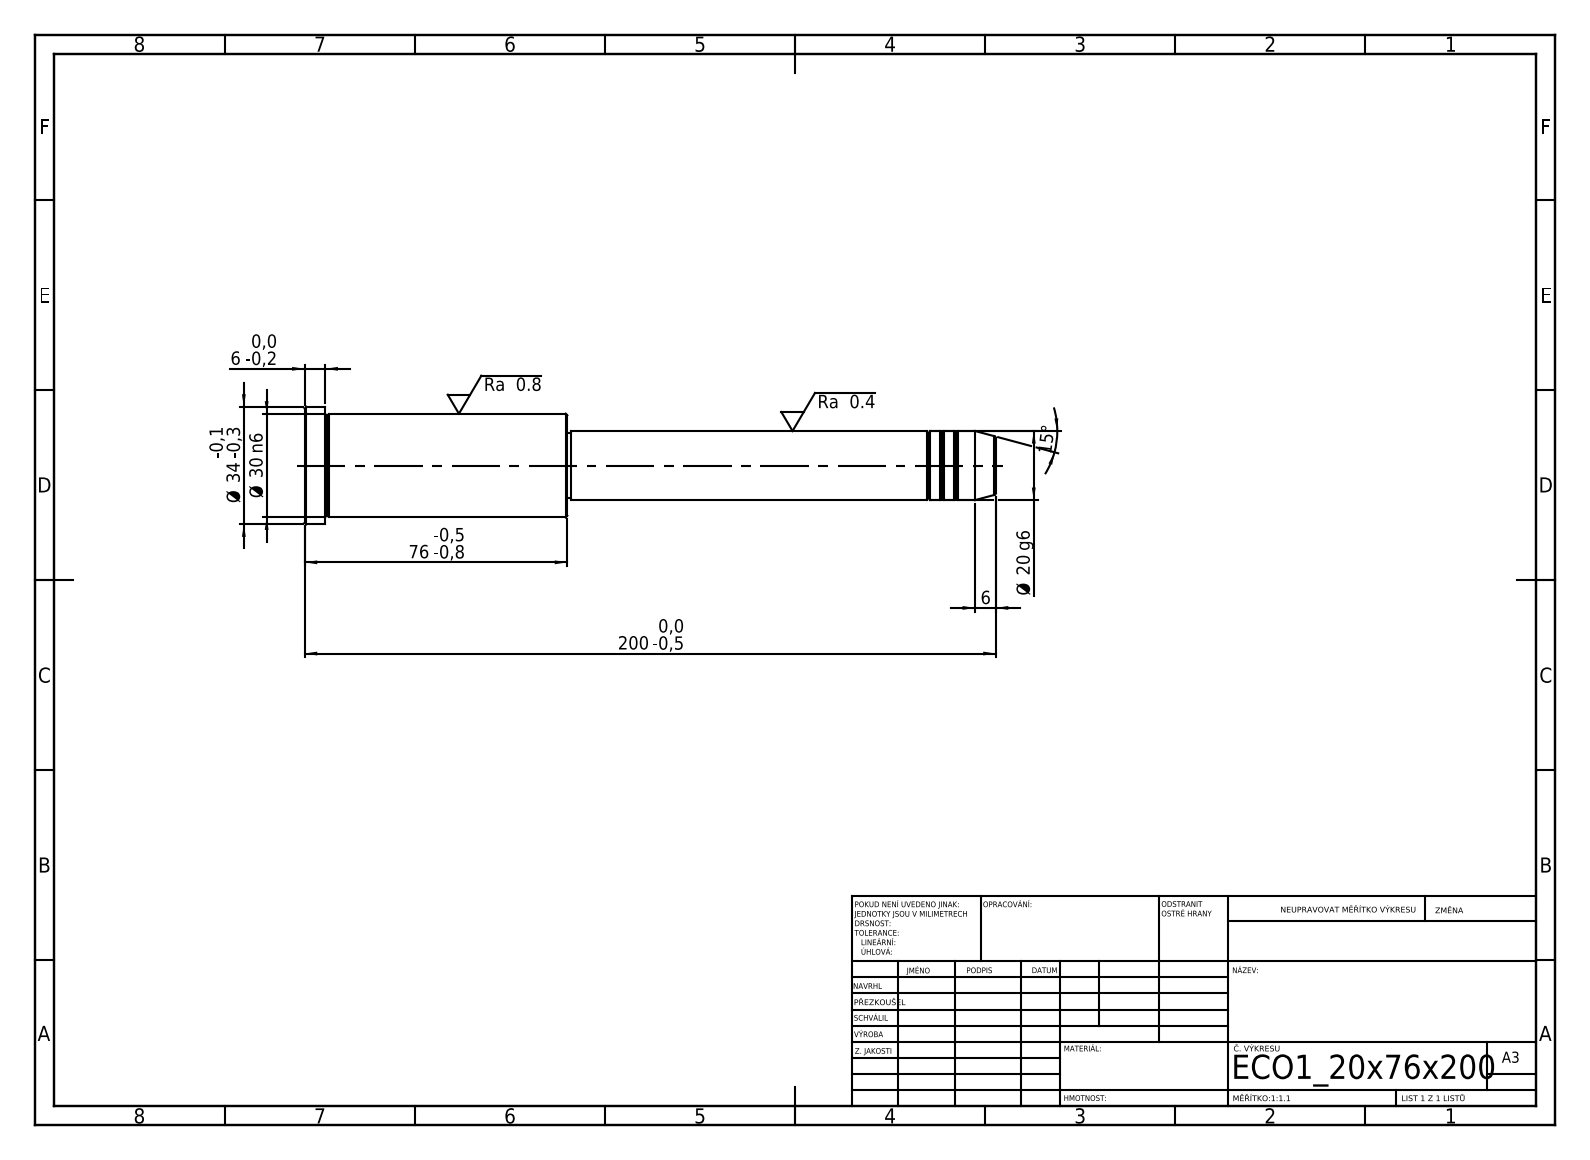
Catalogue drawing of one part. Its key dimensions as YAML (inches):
step_written_by: "SolidWorks 2019 (CONFIG_CONTROL_DESIGN)"
units: inches
bodies: {solids: 1, faces: 43, planar: 5, cylindrical: 14, other: 24}
overall_size: [7.874, 1.339, 1.339]
volume: 5.702
surface_area: 26.16
round_bosses_or_shafts:
  - {diameter: 1.339, count: 1}
  - {diameter: 1.181, count: 1}
  - {diameter: 0.787, count: 1}
  - {diameter: 0.748, count: 1}
face_to_face_distances: [2.992, 4.882, 7.874, 7.638, 2.756, 0.236, 4.843, 0.039, 2.795, 3.031]
